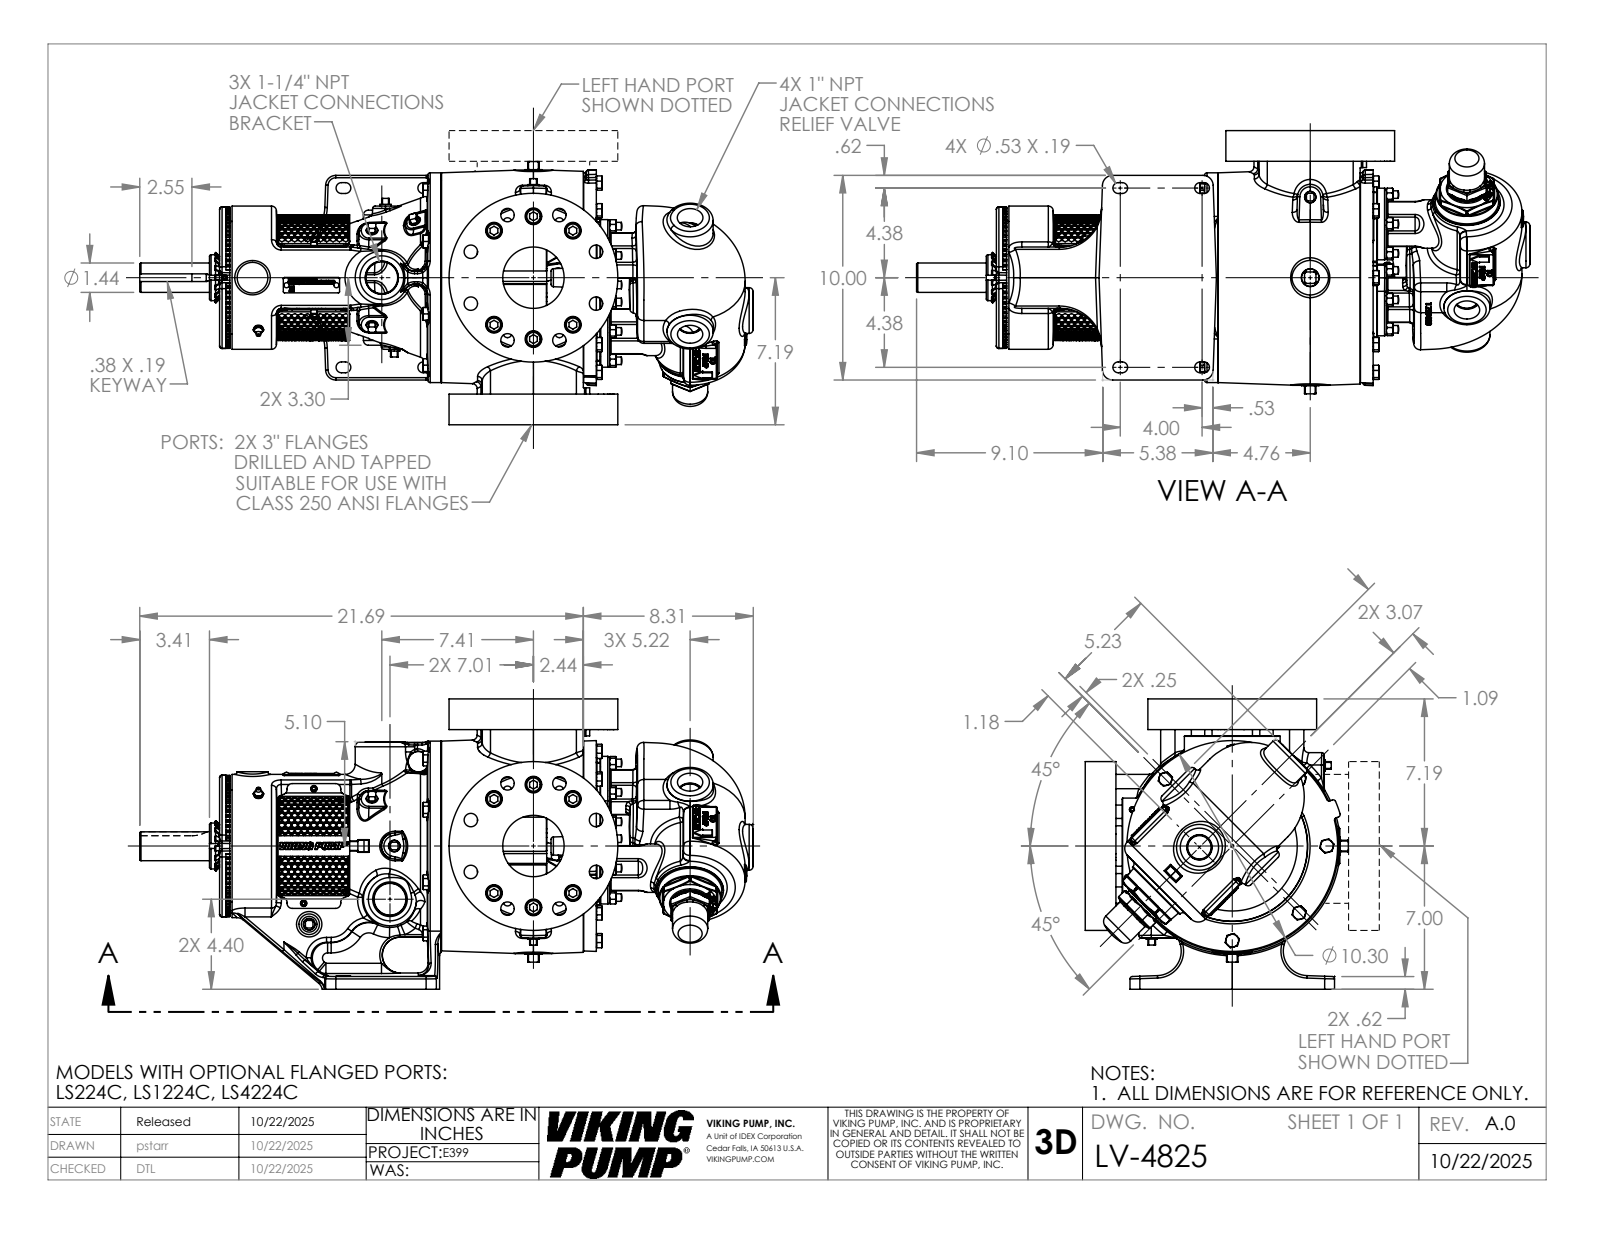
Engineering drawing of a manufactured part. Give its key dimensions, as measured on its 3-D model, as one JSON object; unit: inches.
{"part_name": "LV-4825", "step_written_by": "SolidWorks 2024 (AUTOMOTIVE_DESIGN)", "units": "inches", "bodies": {"solids": 1, "faces": 5853, "planar": 1931, "cylindrical": 981, "other": 2941}, "overall_size": [29.994, 14.188, 12.863], "volume_in3": 1438, "surface_area_in2": 1758, "round_holes": [[0.656, 16], [0.812, 12], [0.25, 9], [1.094, 8], [0.199, 6], [0.159, 3], [0.266, 2], [0.313, 2], [3, 2], [0.453, 1], [1.506, 1], [1.577, 1]], "round_bosses_or_shafts": [[0.75, 12], [0.625, 10], [0.369, 8], [0.625, 6], [3.5, 3], [0.312, 3], [0.19, 3], [8.25, 2]], "partial_cylinders_radius": [[0.063, 109], [0.12, 84], [0.069, 74], [0.03, 36], [0.5, 36], [0.24, 16], [1, 16], [0.19, 14]], "face_to_face_distances": [1.5, 14.187, 12.687, 2.25, 12.128, 0.5, 3.541, 15.669, 2.75, 0.1], "hole_center_spacings": [3, 3.313, 4.685, 6.12, 1.375, 1.009, 1.269, 1.531]}
